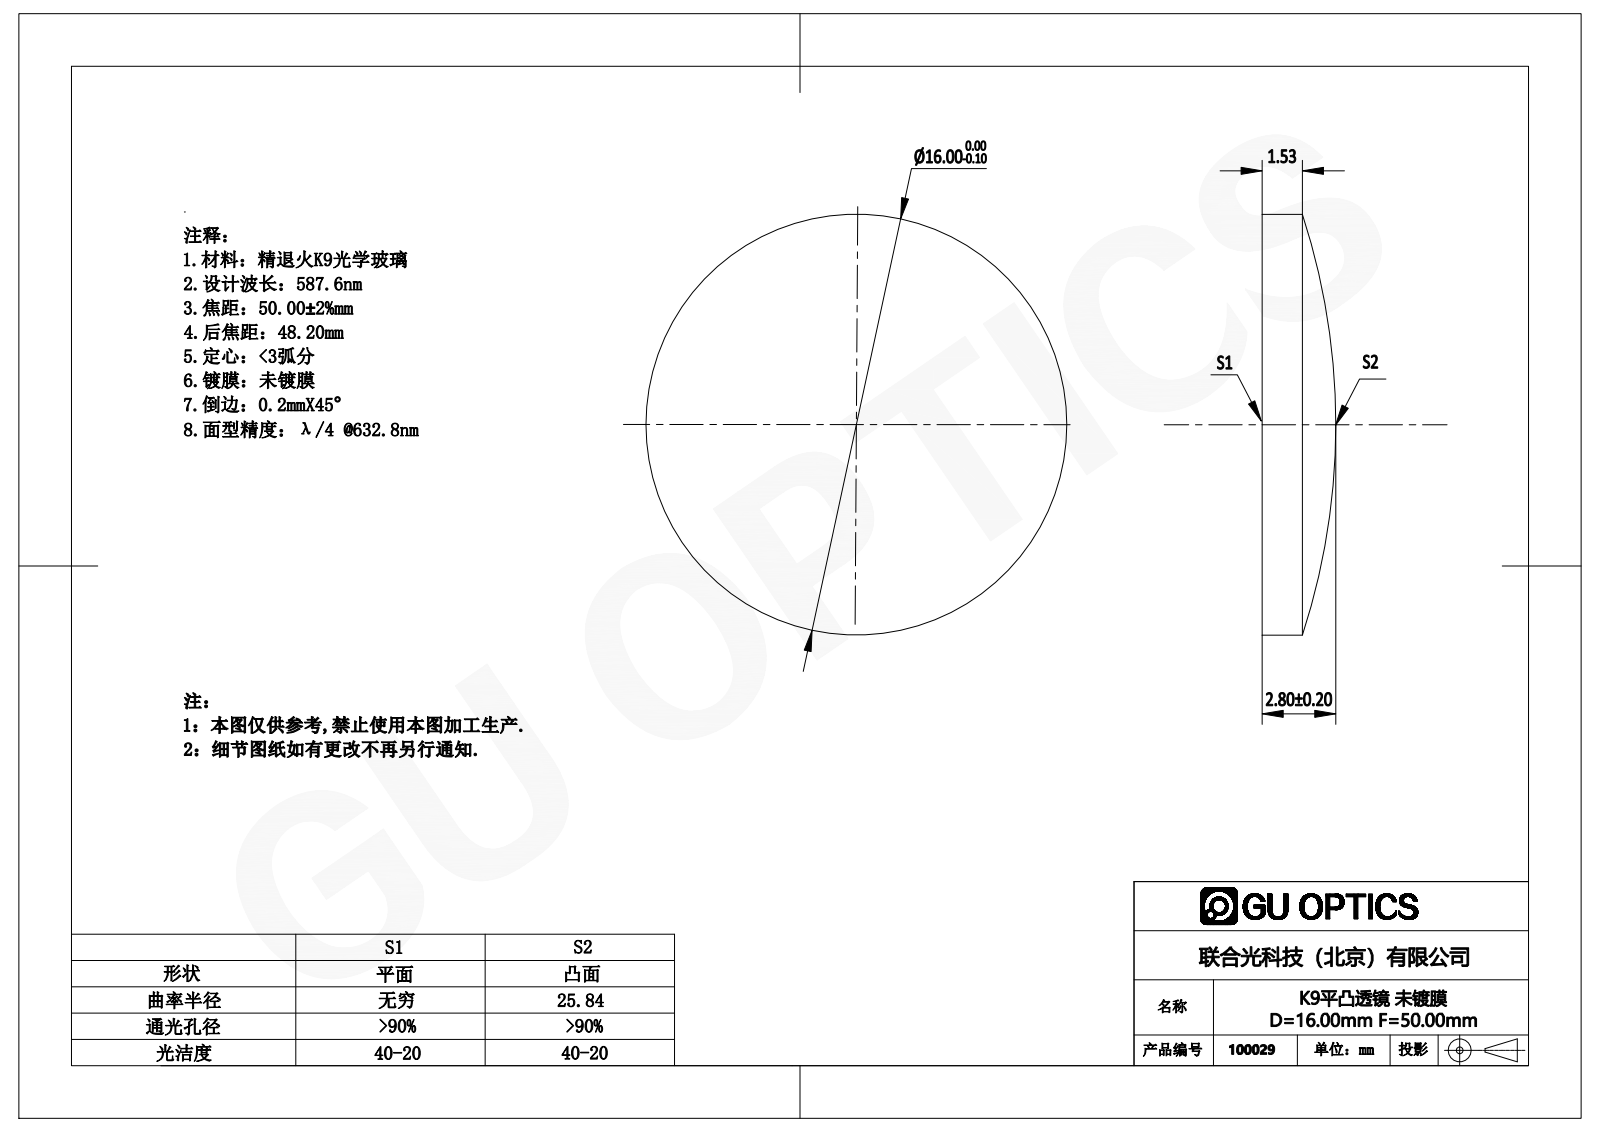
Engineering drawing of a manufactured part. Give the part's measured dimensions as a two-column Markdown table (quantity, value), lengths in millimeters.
| quantity | value |
| --- | --- |
| part name | 100029 |
| STEP written by | SolidWorks 2016 (AUTOMOTIVE_DESIGN) |
| units | millimeters |
| bodies | 1 solid, 5 faces (1 planar, 2 cylindrical, 2 other) |
| overall size | 16 × 16 × 2.8 |
| volume | 436 mm³ |
| surface area | 484 mm² |
| round bosses / shafts (diameter × count) | 16 × 1 |
